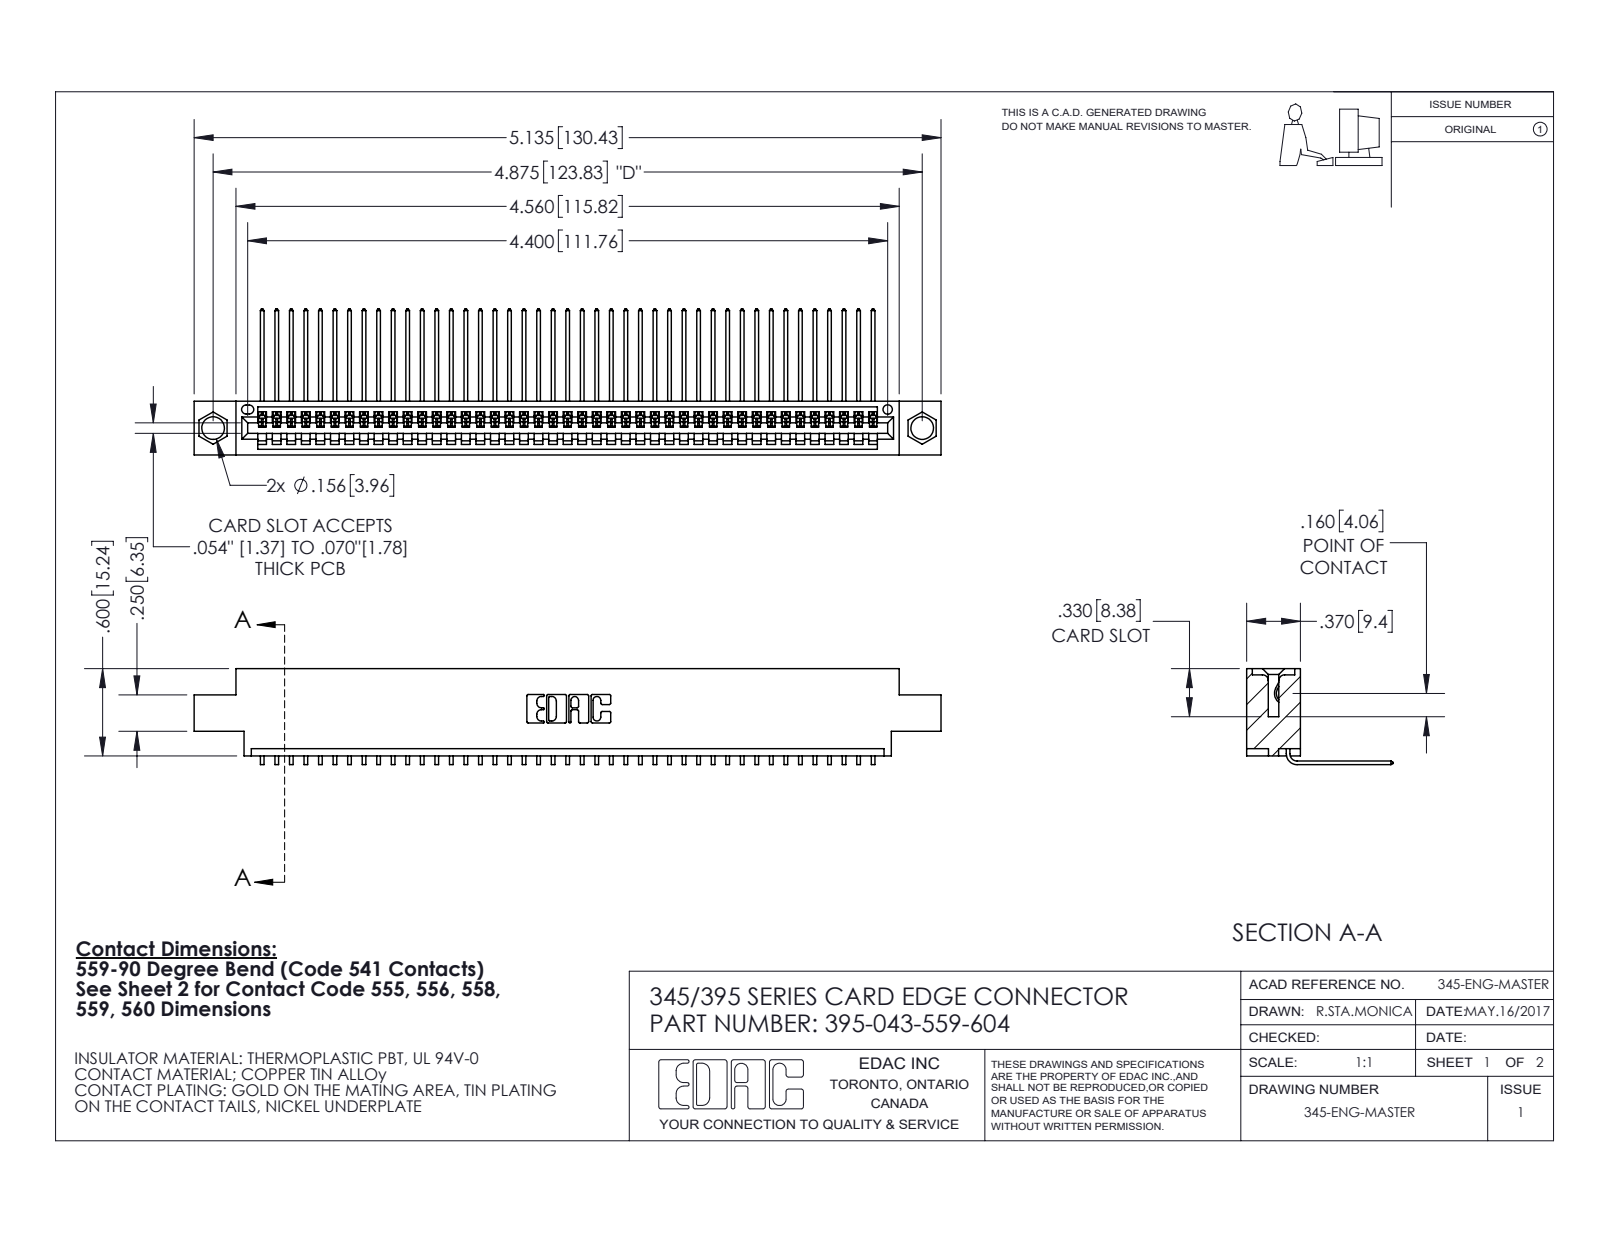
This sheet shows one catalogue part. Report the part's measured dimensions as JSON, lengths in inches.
{"part_name": "395-043-559-604; 345 Part_0.170 Offset - 0.156 Dia-TI; 345-292-001_558 559 Tail - 1", "step_written_by": "SolidWorks 2020 (CONFIG_CONTROL_DESIGN)", "units": "inches", "bodies": {"solids": 44, "faces": 2724, "planar": 1904, "cylindrical": 820, "other": 0}, "overall_size": [5.135, 1.005, 0.659], "volume_in3": 0.752, "surface_area_in2": 26.66, "round_holes": [[0.156, 2], [0.064, 1]], "partial_cylinders_radius": [[0.006, 86], [0.01, 22], [0.007, 6], [0.031, 6], [0.026, 3], [0.031, 2], [0.04, 2], [0.014, 1]], "face_to_face_distances": [0.072, 0.298, 0.37, 0.2, 0.098, 0.272, 0.025, 0.225, 0.175, 0.149], "hole_center_spacings": [0.27, 4.639, 4.875]}
